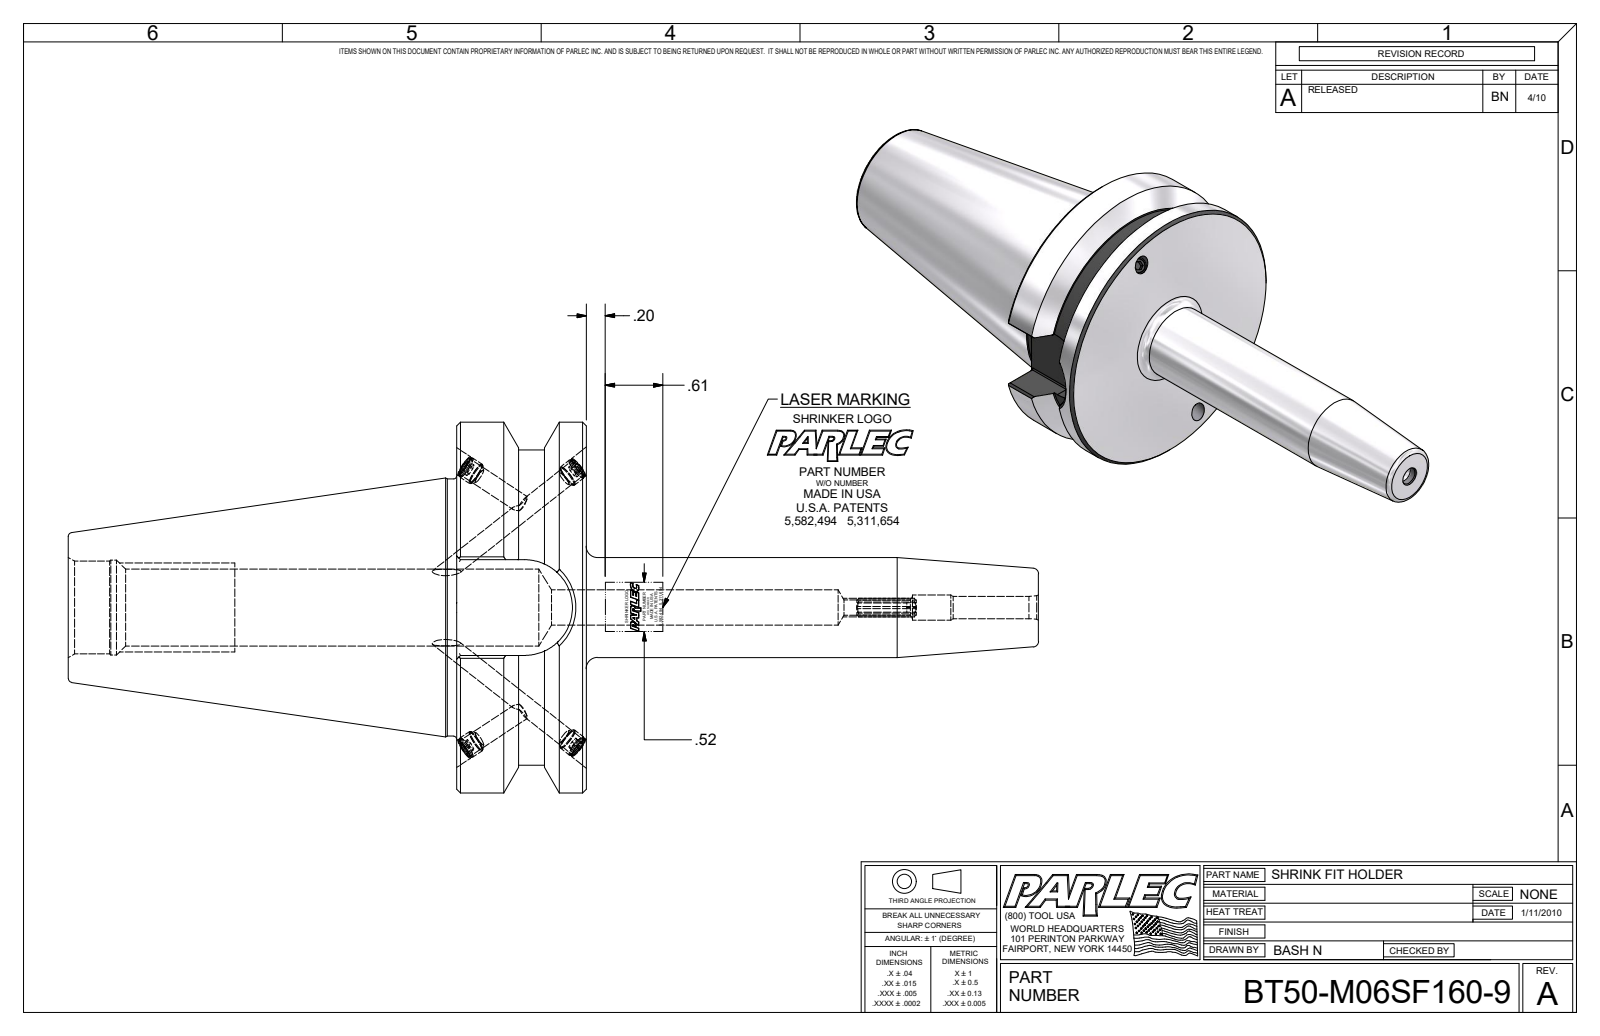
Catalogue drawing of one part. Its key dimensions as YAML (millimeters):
part_name: "BT50-M06SF160-9; BT50BC-M06SF160-9-1; 029-966; BS-SFM058-16"
step_written_by: "Autodesk Inventor 2009 (AUTOMOTIVE_DESIGN)"
units: millimeters
bodies: {solids: 6, faces: 174, planar: 79, cylindrical: 42, other: 53}
overall_size: [261.8, 100, 100]
volume: 503900
surface_area: 69030
round_holes:
  - {diameter: 5, count: 4}
  - {diameter: 6.1, count: 4}
  - {diameter: 6, count: 1}
  - {diameter: 6.8, count: 1}
  - {diameter: 25.6, count: 1}
round_bosses_or_shafts:
  - {diameter: 6.2, count: 4}
  - {diameter: 6, count: 4}
  - {diameter: 100, count: 1}
  - {diameter: 85, count: 1}
  - {diameter: 69.3, count: 1}
  - {diameter: 27, count: 1}
partial_cylinders:
  - {radius: 0.5, count: 8}
  - {radius: 2.5, count: 1}
  - {radius: 12.9, count: 1}
face_to_face_distances: [35, 70.8, 104.8, 139.8, 25.8, 261.8, 157, 122, 128.5, 23.7]
